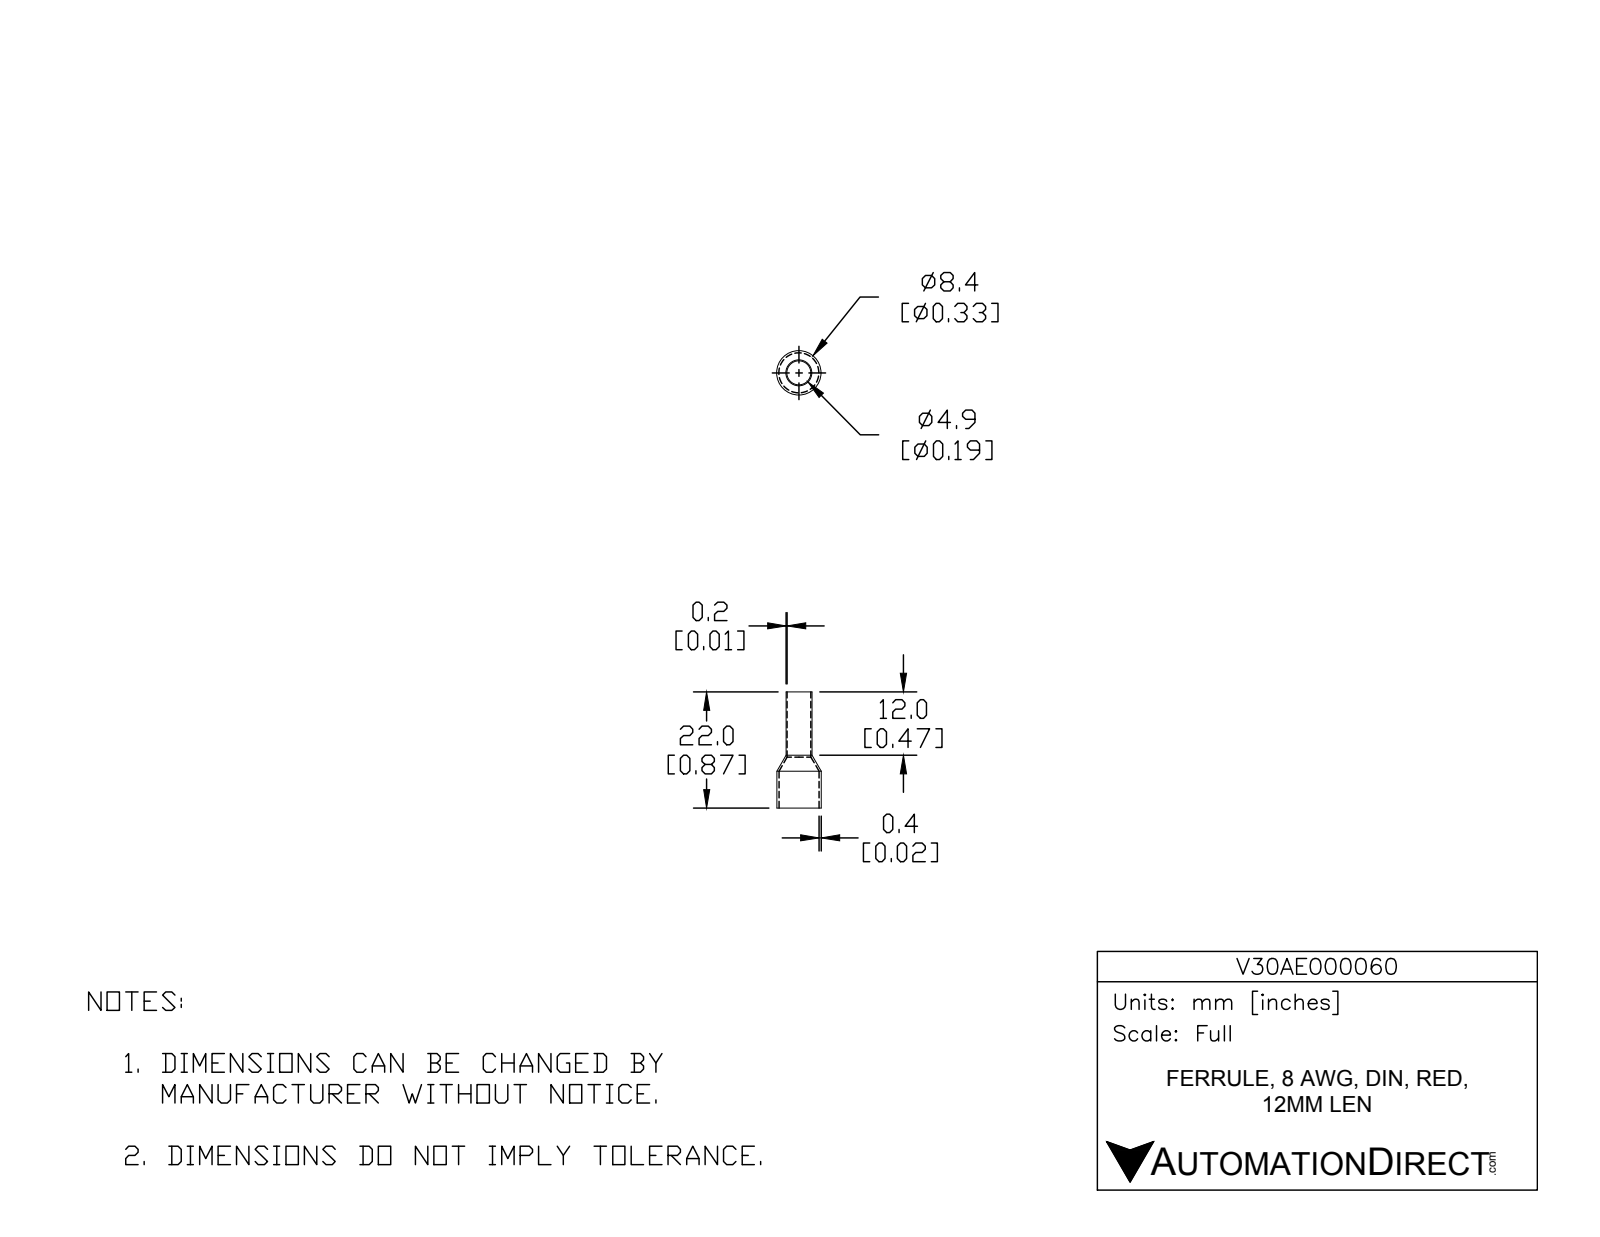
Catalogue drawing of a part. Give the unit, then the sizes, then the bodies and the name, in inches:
Units: inches
Overall size (bounding box): 0.866 × 0.331 × 0.331
Round holes (diameter × count): ⌀0.177 ×1, ⌀0.299 ×1
Round bosses / shafts (diameter × count): ⌀0.331 ×1, ⌀0.193 ×1
Main face-to-face distances: 0.866
Volume: 0.008 in³ · Surface area: 1.33 in²
Bodies: 1 solid, 14 faces (2 planar, 8 cylindrical, 4 other)
Part name (STEP PRODUCT): V30AE000060
STEP written by: SolidWorks 2017 (AUTOMOTIVE_DESIGN)
